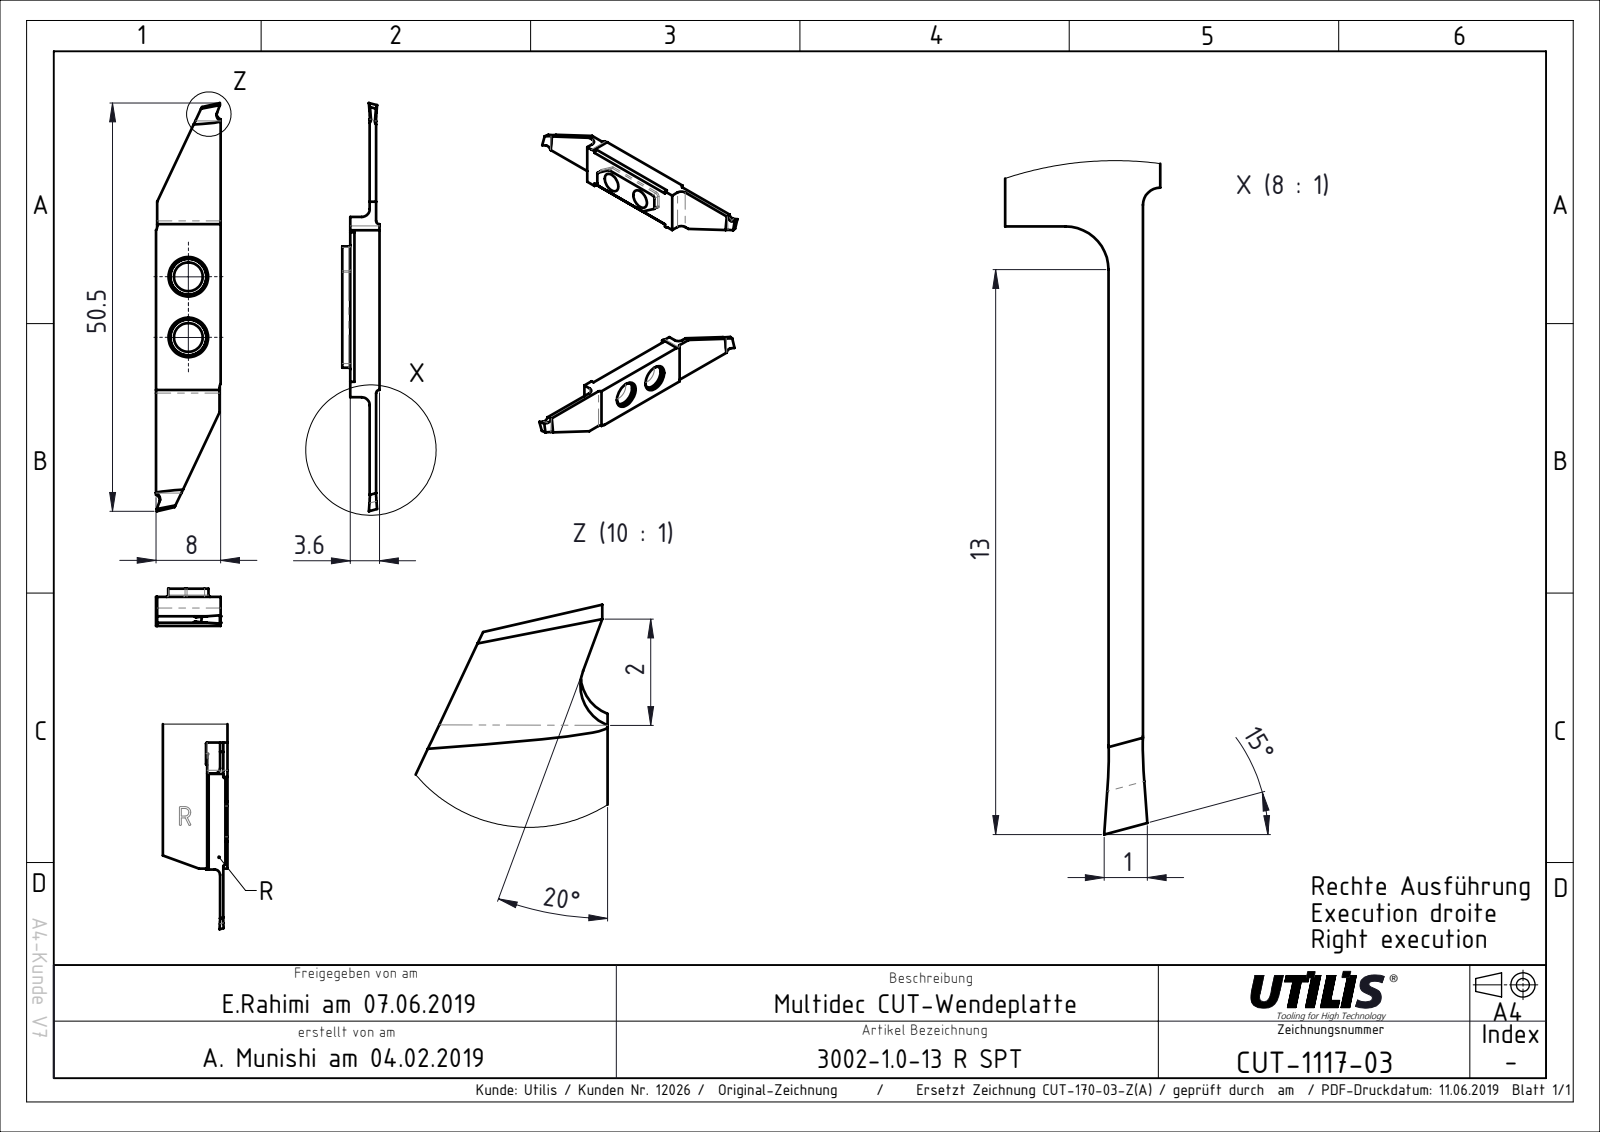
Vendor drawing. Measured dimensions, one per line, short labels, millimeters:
name: CUT-1117; ASME Y14.5
written by: FormatWorks Professional (AP242_MANAGED_MODEL_BASED_3D_ENGINEERING_MIM_LF)
unit: mm
bodies: 1 solid, 38 faces (28 planar, 10 cylindrical, 0 other)
size: 50.5 × 8 × 3.6
volume: 682 mm³; area: 933 mm²
holes: 2× ⌀3.55
rounds: 4× R1, 2× R0.4
face distances: 0.41, 3.19, 3.6, 2.41, 0.78, 1.19, 8, 22.3, 7.85, 18.09
hole spacings: 7.5
